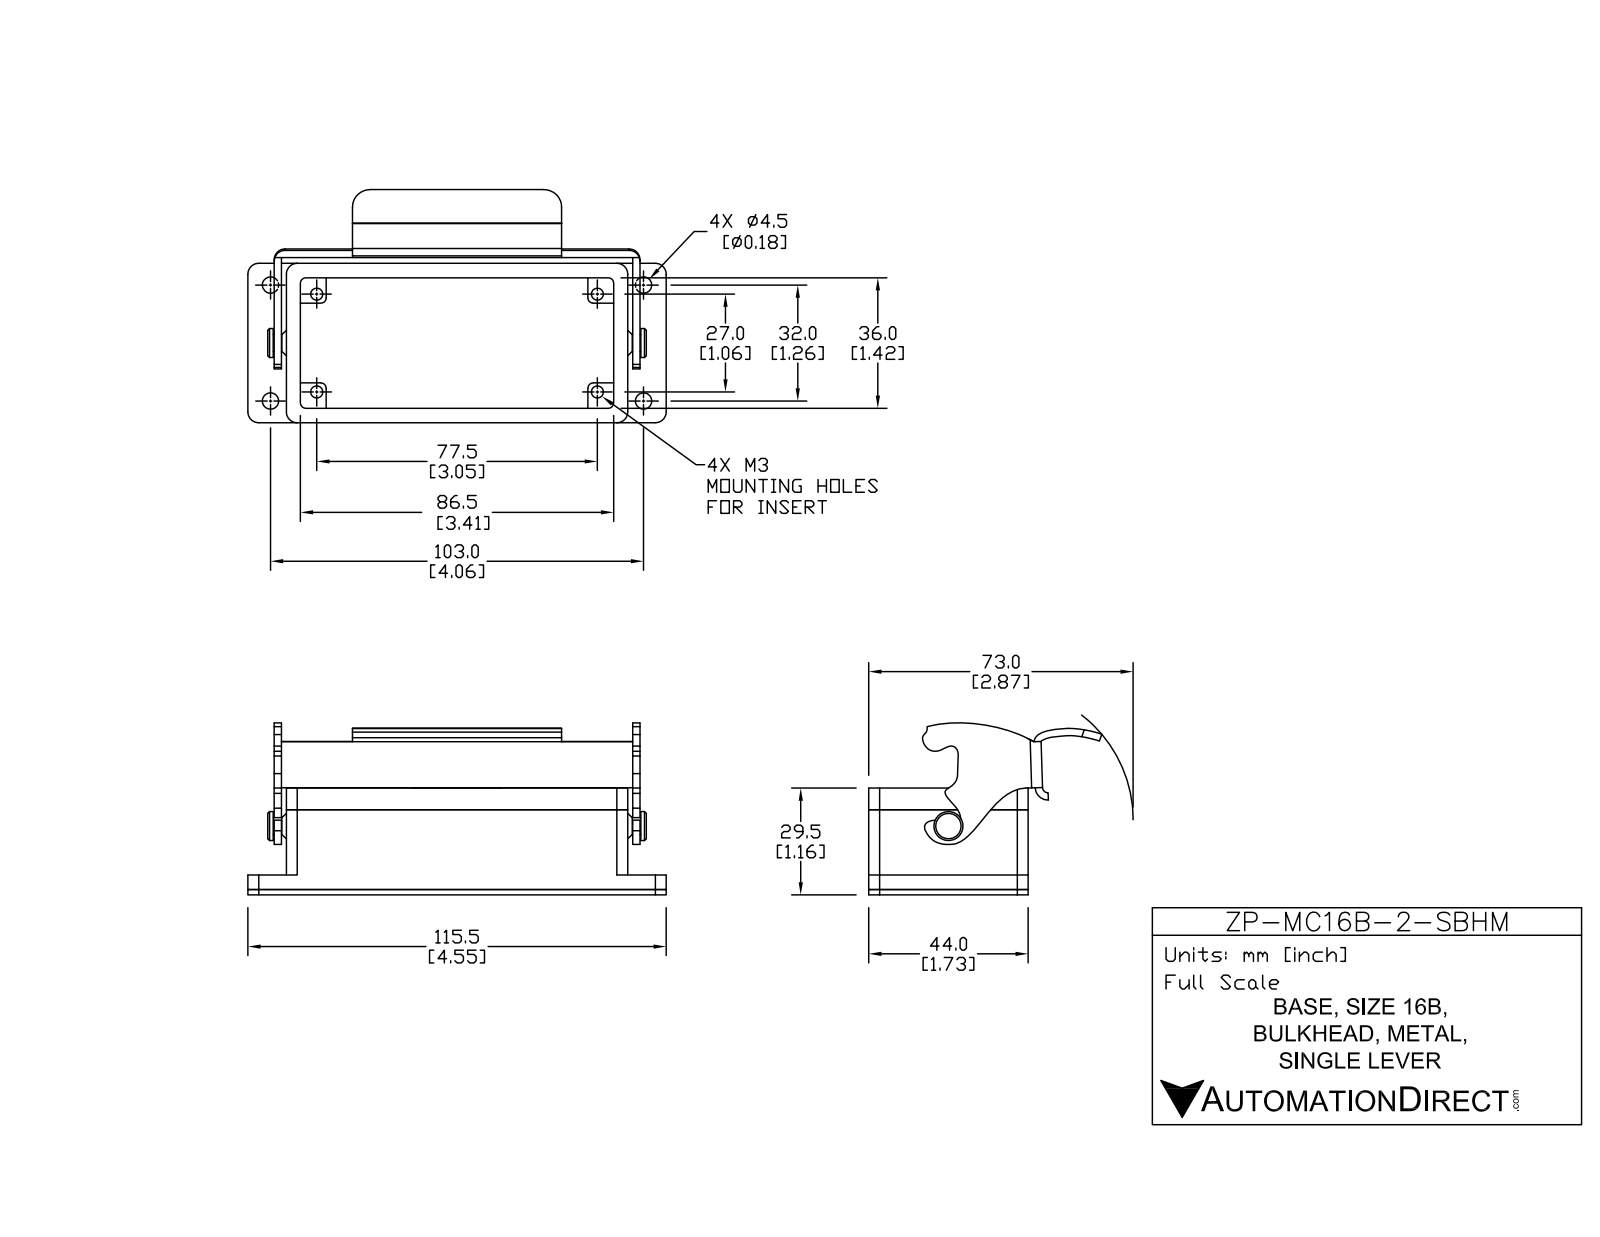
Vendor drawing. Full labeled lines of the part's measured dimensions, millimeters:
Part name (STEP PRODUCT): ZP-MC16B-2-SBHM
STEP written by: SolidWorks 2011 (AUTOMOTIVE_DESIGN)
Units: millimetres
Bodies: 4 solids, 208 faces (92 planar, 112 cylindrical, 4 other)
Overall size (bounding box): 115.5 × 69.96 × 44.44
Volume: 36 879 mm³ · Surface area: 32 938 mm²
Round holes (diameter × count): ⌀3.3 ×4, ⌀4.5 ×4
Round bosses / shafts (diameter × count): ⌀8 ×1, ⌀4.67 ×1
Partial cylindrical surfaces — rounded edges, fillets, slot ends (radius × count): R0.5 ×13, R1.5 ×12, R3 ×9, R2 ×3, R4 ×3, R1 ×2, R10 ×2, R0.92 ×1
Main face-to-face distances: 3, 4, 44, 41, 40, 1, 37, 22, 1.5, 23.5
Hole centre spacings: 13.24, 32.24, 90.03, 94.71, 27, 32, 77, 81.6
